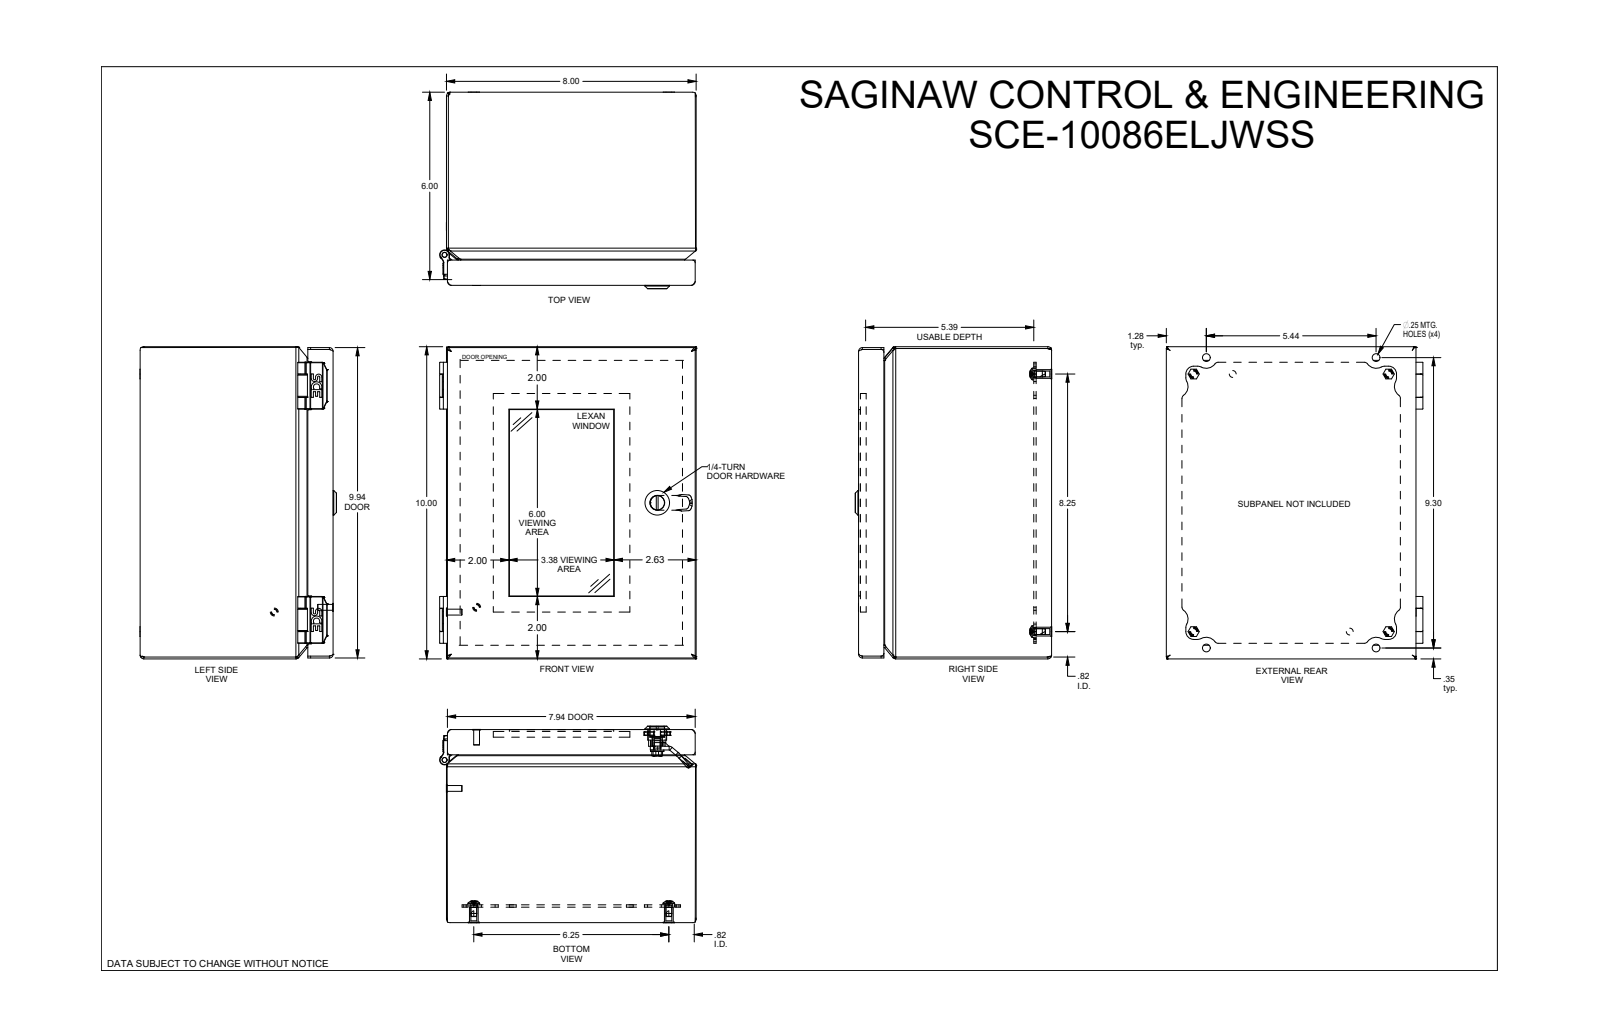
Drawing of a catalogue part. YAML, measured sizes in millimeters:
part_name: "SCE-10086ELJW"
step_written_by: "SolidWorks 2019 (AUTOMOTIVE_DESIGN)"
units: millimeters
bodies: {solids: 31, faces: 931, planar: 365, cylindrical: 302, other: 264}
overall_size: [254, 208.8, 159.9]
volume: 521400
surface_area: 649000
round_holes:
  - {diameter: 4.8, count: 4}
  - {diameter: 6.4, count: 4}
  - {diameter: 7.2, count: 4}
  - {diameter: 0.5, count: 2}
  - {diameter: 2.5, count: 2}
  - {diameter: 5.5, count: 2}
  - {diameter: 4, count: 1}
  - {diameter: 5.1, count: 1}
  - {diameter: 6.1, count: 1}
  - {diameter: 6.5, count: 1}
  - {diameter: 6.8, count: 1}
  - {diameter: 7.2, count: 1}
round_bosses_or_shafts:
  - {diameter: 4.8, count: 6}
  - {diameter: 9.5, count: 4}
  - {diameter: 7.1, count: 4}
  - {diameter: 4.1, count: 4}
  - {diameter: 6.6, count: 2}
  - {diameter: 6.5, count: 2}
  - {diameter: 6, count: 2}
  - {diameter: 5.8, count: 2}
partial_cylinders:
  - {radius: 0.8, count: 28}
  - {radius: 1.3, count: 24}
  - {radius: 0.3, count: 21}
  - {radius: 6.4, count: 13}
  - {radius: 3.2, count: 11}
  - {radius: 0.3, count: 10}
  - {radius: 8.7, count: 8}
  - {radius: 0.6, count: 5}
face_to_face_distances: [1.5, 155.7, 154.2, 201.7, 252.5, 14.5, 13, 141.1, 12.6, 11.1]
hole_center_spacings: [158.8, 158.8, 262.9, 31.8, 127, 105.2, 182.4, 209.5]
